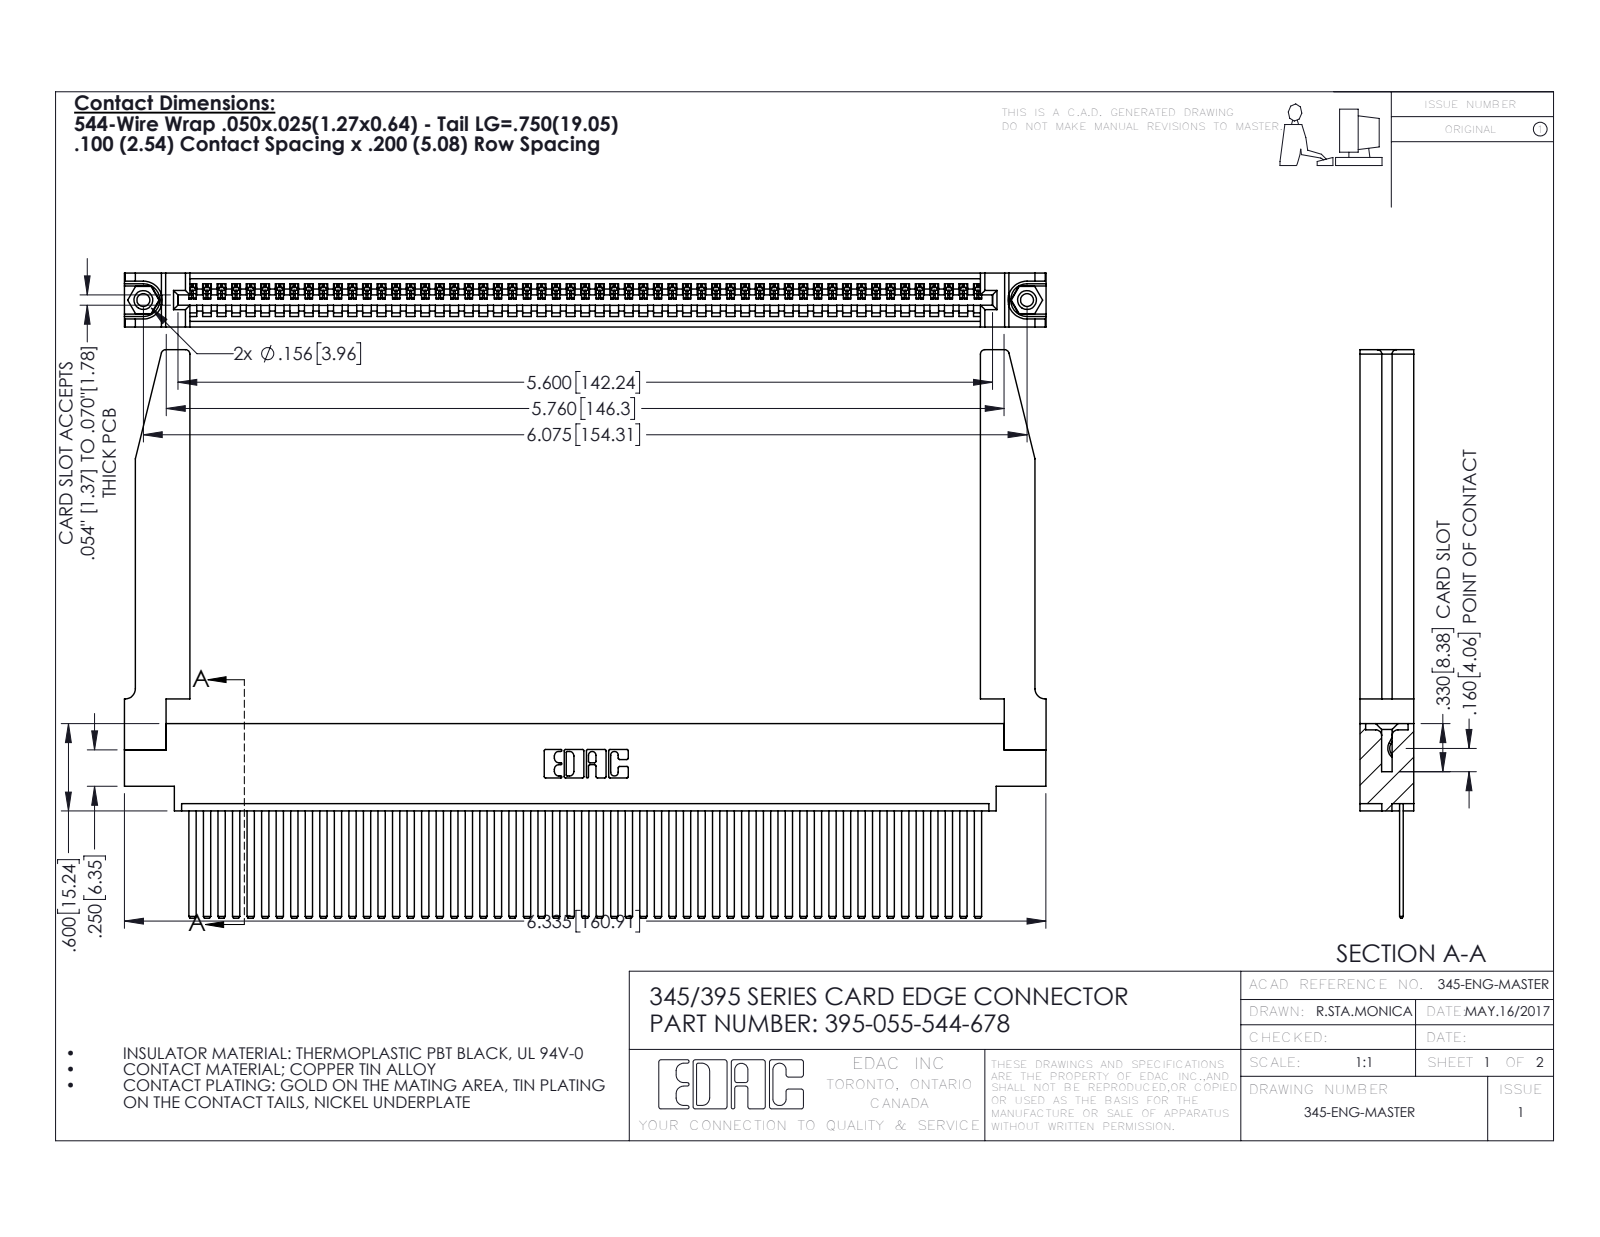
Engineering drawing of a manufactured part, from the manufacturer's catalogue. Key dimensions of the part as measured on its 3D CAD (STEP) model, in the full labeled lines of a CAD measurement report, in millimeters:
Part name (STEP PRODUCT): 345-220-078_345-220-078; 345 Part_0.170 Offset - 0.156 Dia-TH; 395-055-544-678; 345-250-001_345-250-001-102 (+1 more)
STEP written by: SolidWorks 2016 (CONFIG_CONTROL_DESIGN)
Units: millimetres
Bodies: 60 solids, 3224 faces (2206 planar, 966 cylindrical, 52 other)
Overall size (bounding box): 160.9 × 99.2 × 9.4
Volume: 23 680 mm³ · Surface area: 30 210 mm²
Round holes (diameter × count): ⌀2.3 ×2, ⌀3.2 ×2, ⌀4 ×2, ⌀1.6 ×1
Round bosses / shafts (diameter × count): ⌀3.9 ×2
Partial cylindrical surfaces — rounded edges, fillets, slot ends (radius × count): R0.2 ×110, R0.3 ×22, R0.8 ×8, R0.2 ×6, R0.8 ×6, R0.7 ×3, R0.8 ×2, R1 ×2
Main face-to-face distances: 1.8, 7.6, 9.4, 2.5, 6.9, 0.6, 5.1, 5.7, 3.8, 3.8
Hole centre spacings: 6.9, 148.3, 154.3
